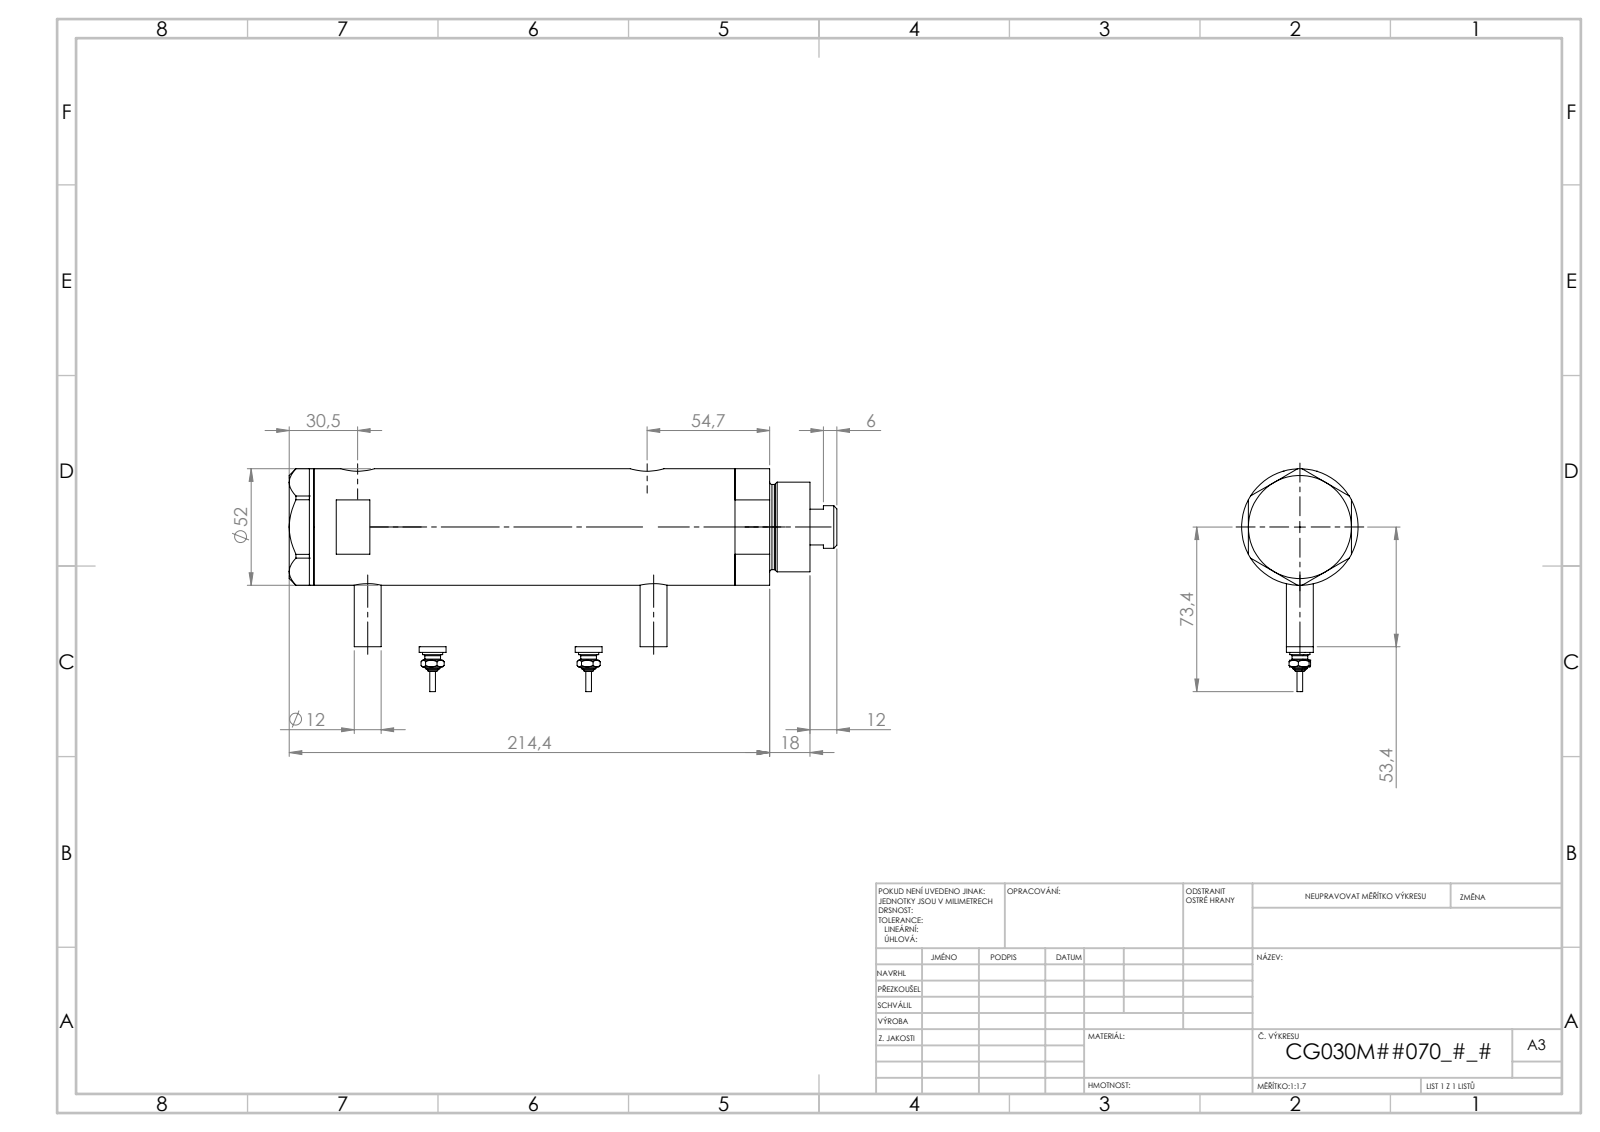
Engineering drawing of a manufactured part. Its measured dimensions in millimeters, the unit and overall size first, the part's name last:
Units: millimetres
Overall size (bounding box): 219.02 × 84.3 × 52
Round holes (diameter × count): ⌀5 ×2, ⌀9.73 ×2, ⌀12.5 ×2, ⌀15 ×2, ⌀6.5 ×1, ⌀20 ×1, ⌀21.5 ×1, ⌀30 ×1, ⌀33 ×1, ⌀44 ×1
Round bosses / shafts (diameter × count): ⌀12 ×3, ⌀9 ×2, ⌀7 ×2, ⌀4.34 ×2, ⌀2.4 ×2, ⌀52 ×1, ⌀40 ×1, ⌀38 ×1
Main face-to-face distances: 123.54, 23.8, 99.74, 11, 34.8, 134.54, 46, 170.94, 159.94, 136.14
Hole centre spacings: 2.9, 4.5, 96.75, 99.65, 101.25, 104.15, 2.89, 2.91
Volume: 391 546 mm³ · Surface area: 89 467 mm²
Bodies: 6 solids, 246 faces (95 planar, 77 cylindrical, 74 other)
Part name (STEP PRODUCT): V270CG_VC; V270CG_MIDDLE; V270CG_FRONT; V270CG_SWITCH (+1 more)
STEP written by: SolidWorks 2019 (CONFIG_CONTROL_DESIGN)
